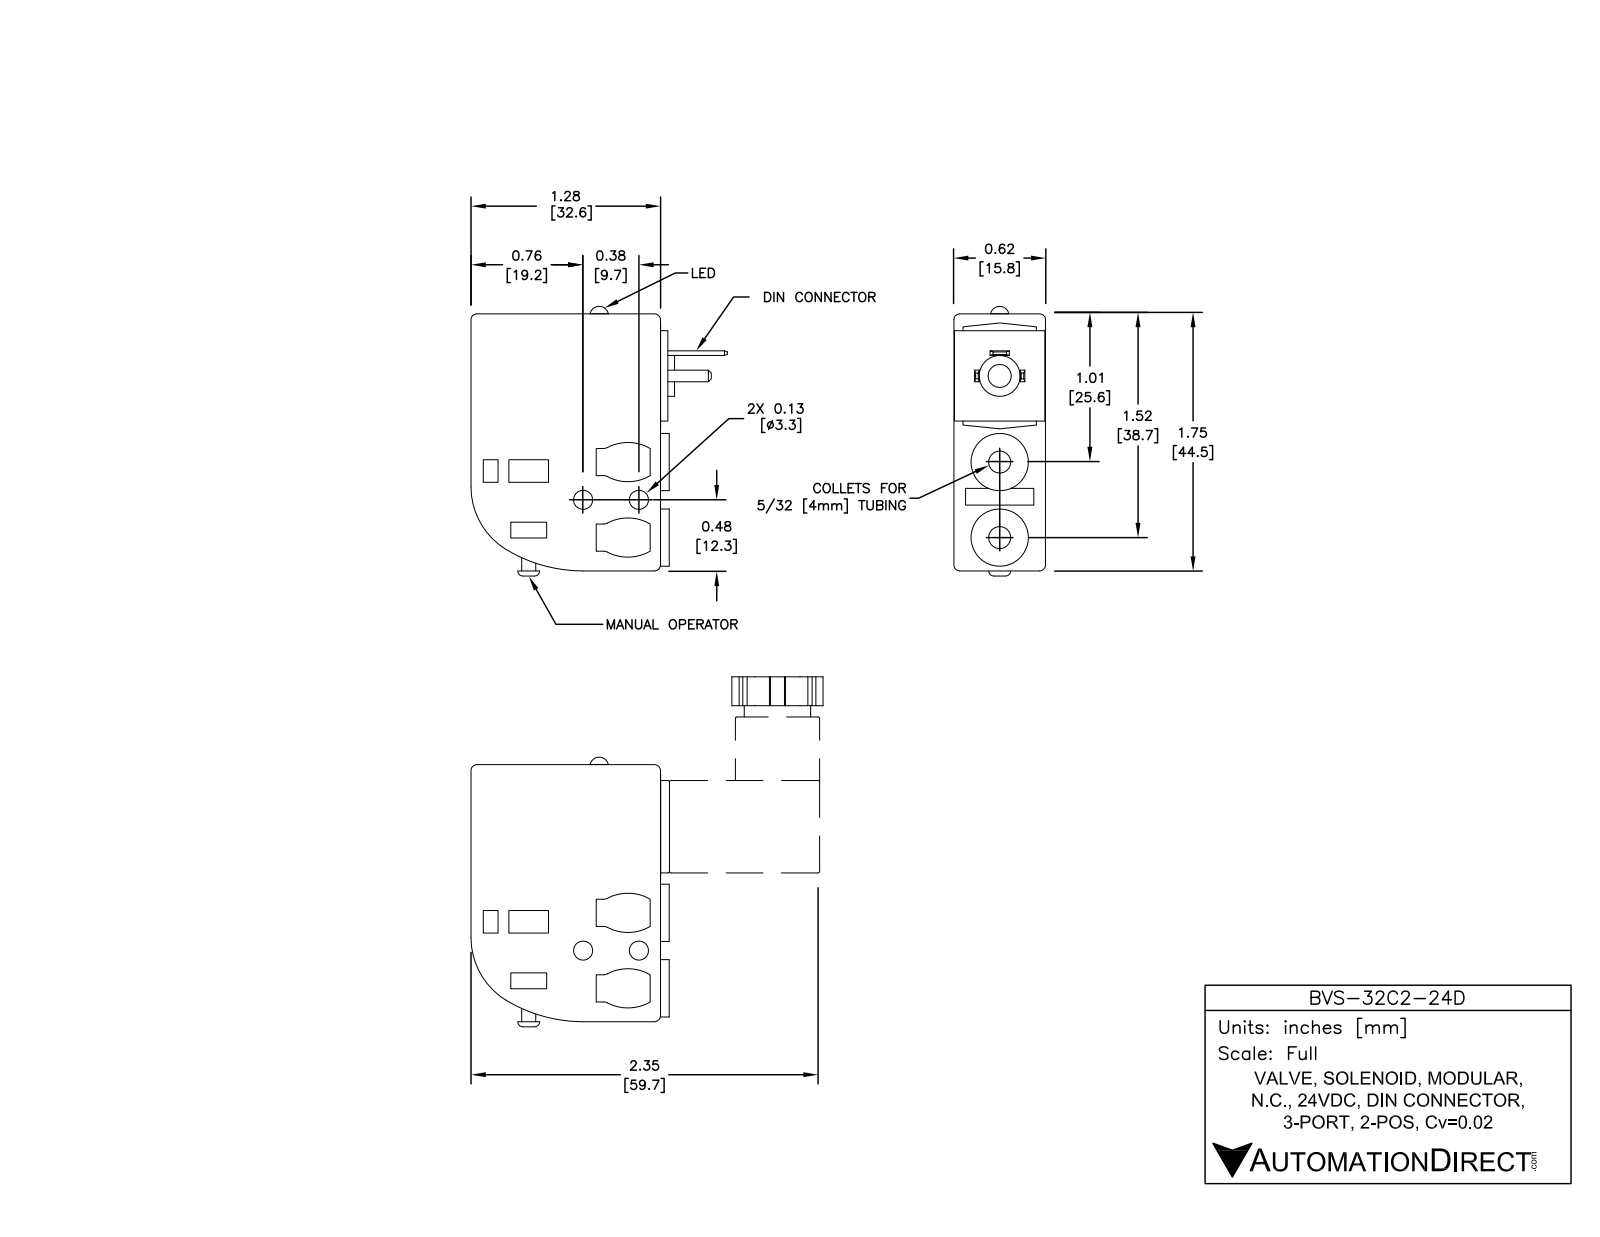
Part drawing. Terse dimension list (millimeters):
name: BVS-32C2-24D
written by: SolidWorks 2013 (AUTOMOTIVE_DESIGN)
unit: mm
bodies: 2 solids, 204 faces (135 planar, 56 cylindrical, 13 other)
size: 46.6 × 44.3 × 15.8
volume: 20 980 mm³; area: 7 097 mm²
holes: 2× ⌀3.3, 2× ⌀3.8, 2× ⌀6.5, 1× ⌀1.2, 1× ⌀4
bosses: 2× ⌀9.9, 1× ⌀7.1, 1× ⌀3.1, 1× ⌀2.4
rounds: 11× R1, 4× R1.3, 4× R7.6, 1× R12.7, 1× R25.4
face distances: 15.8, 2.5, 13.3, 32.7, 1.3, 1.3, 34, 44.5, 32.7, 10.8
hole spacings: 1.5, 9.7, 11.5, 13.1, 14.9, 16.5, 27.9
